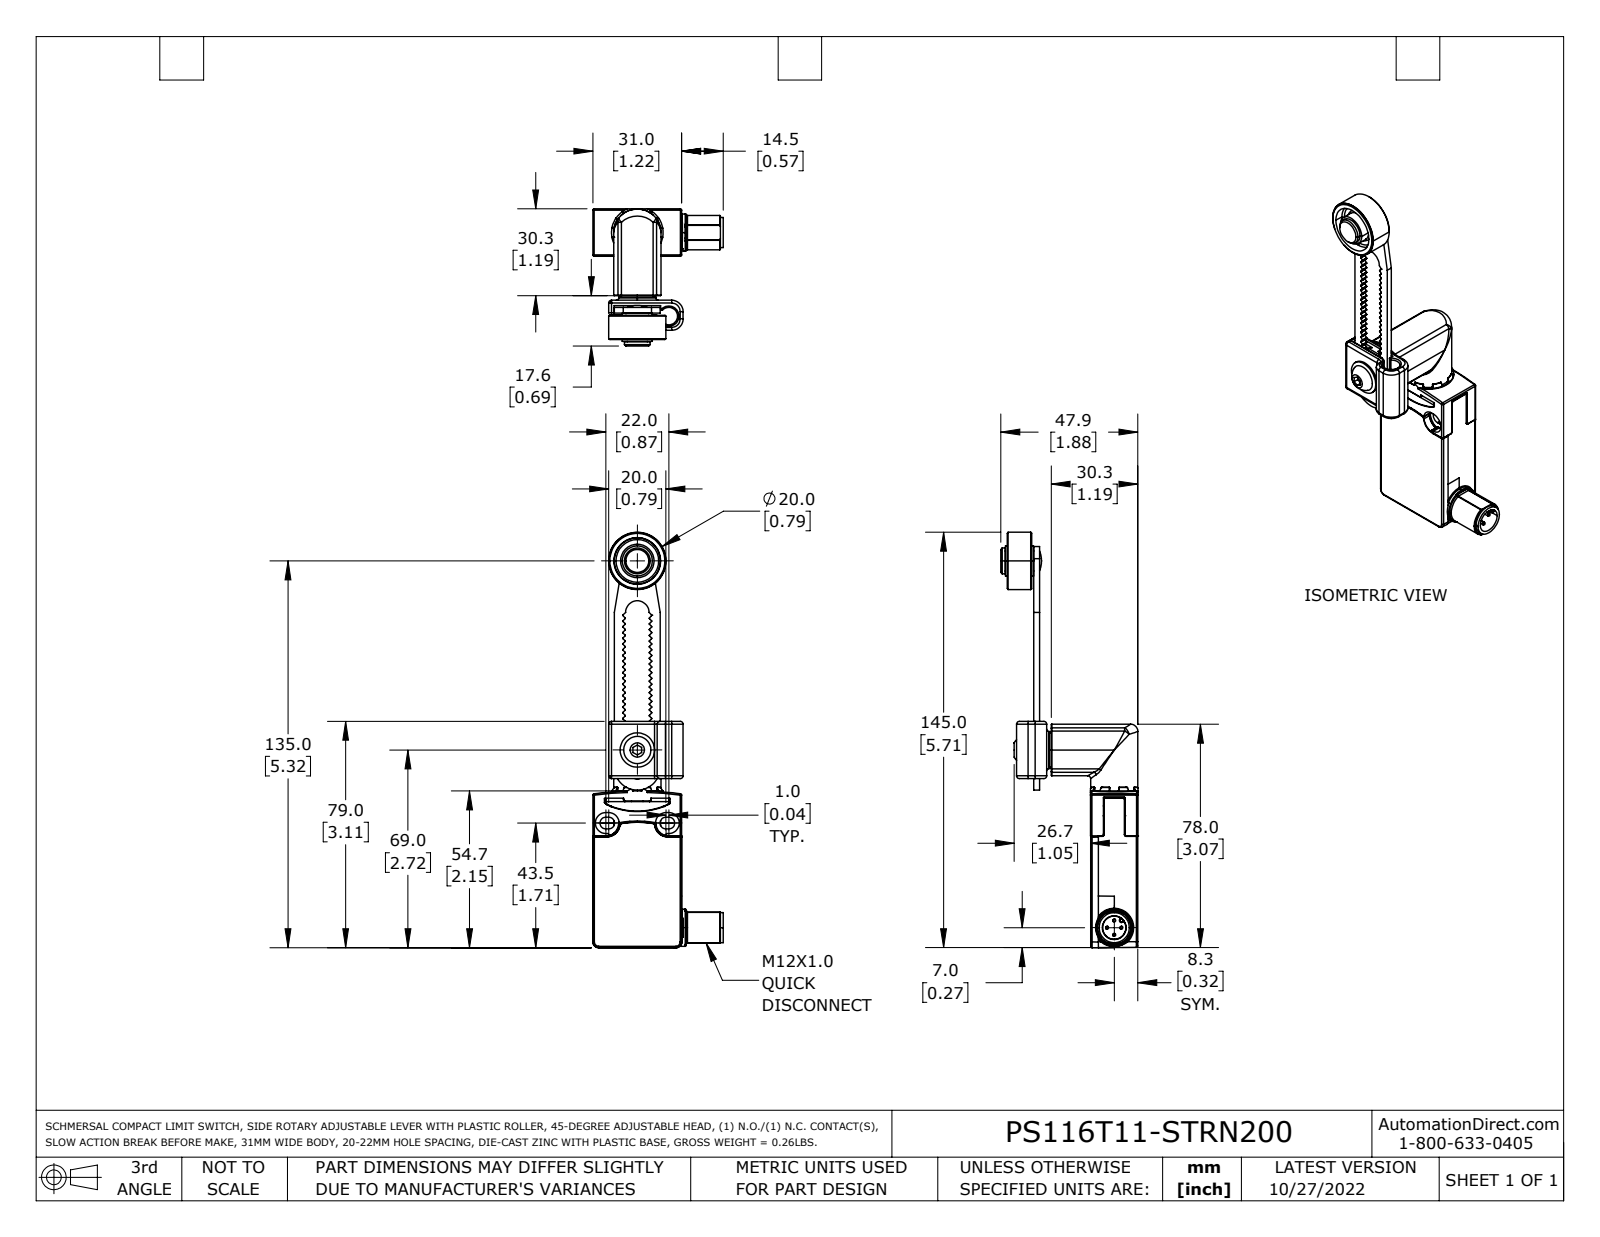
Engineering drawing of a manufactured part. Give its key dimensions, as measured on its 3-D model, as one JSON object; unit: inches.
{"part_name": "PS116T11-STRN200_Default", "step_written_by": "SolidWorks 2021 (CONFIG_CONTROL_DESIGN)", "units": "inches", "bodies": {"solids": 1, "faces": 1431, "planar": 446, "cylindrical": 686, "other": 299}, "overall_size": [5.71, 1.886, 1.791], "volume_in3": 2.583, "surface_area_in2": 32.08, "round_holes": [[0.079, 1], [0.24, 1], [0.315, 1], [0.327, 1], [0.48, 1], [0.571, 1], [0.583, 1]], "round_bosses_or_shafts": [[0.039, 4], [0.512, 2], [0.413, 2], [0.787, 1], [0.65, 1], [0.567, 1], [0.524, 1], [0.475, 1]], "partial_cylinders_radius": [[0.008, 229], [0.004, 67], [0.02, 41], [0.039, 27], [0.079, 12], [0.014, 10], [0.118, 5], [0.081, 4]], "face_to_face_distances": [0.65, 0.781, 0.079, 1.431, 1.352, 0.703, 0.652, 0.201, 0.098, 0.177], "hole_center_spacings": [1.227, 1.615, 2.598]}
